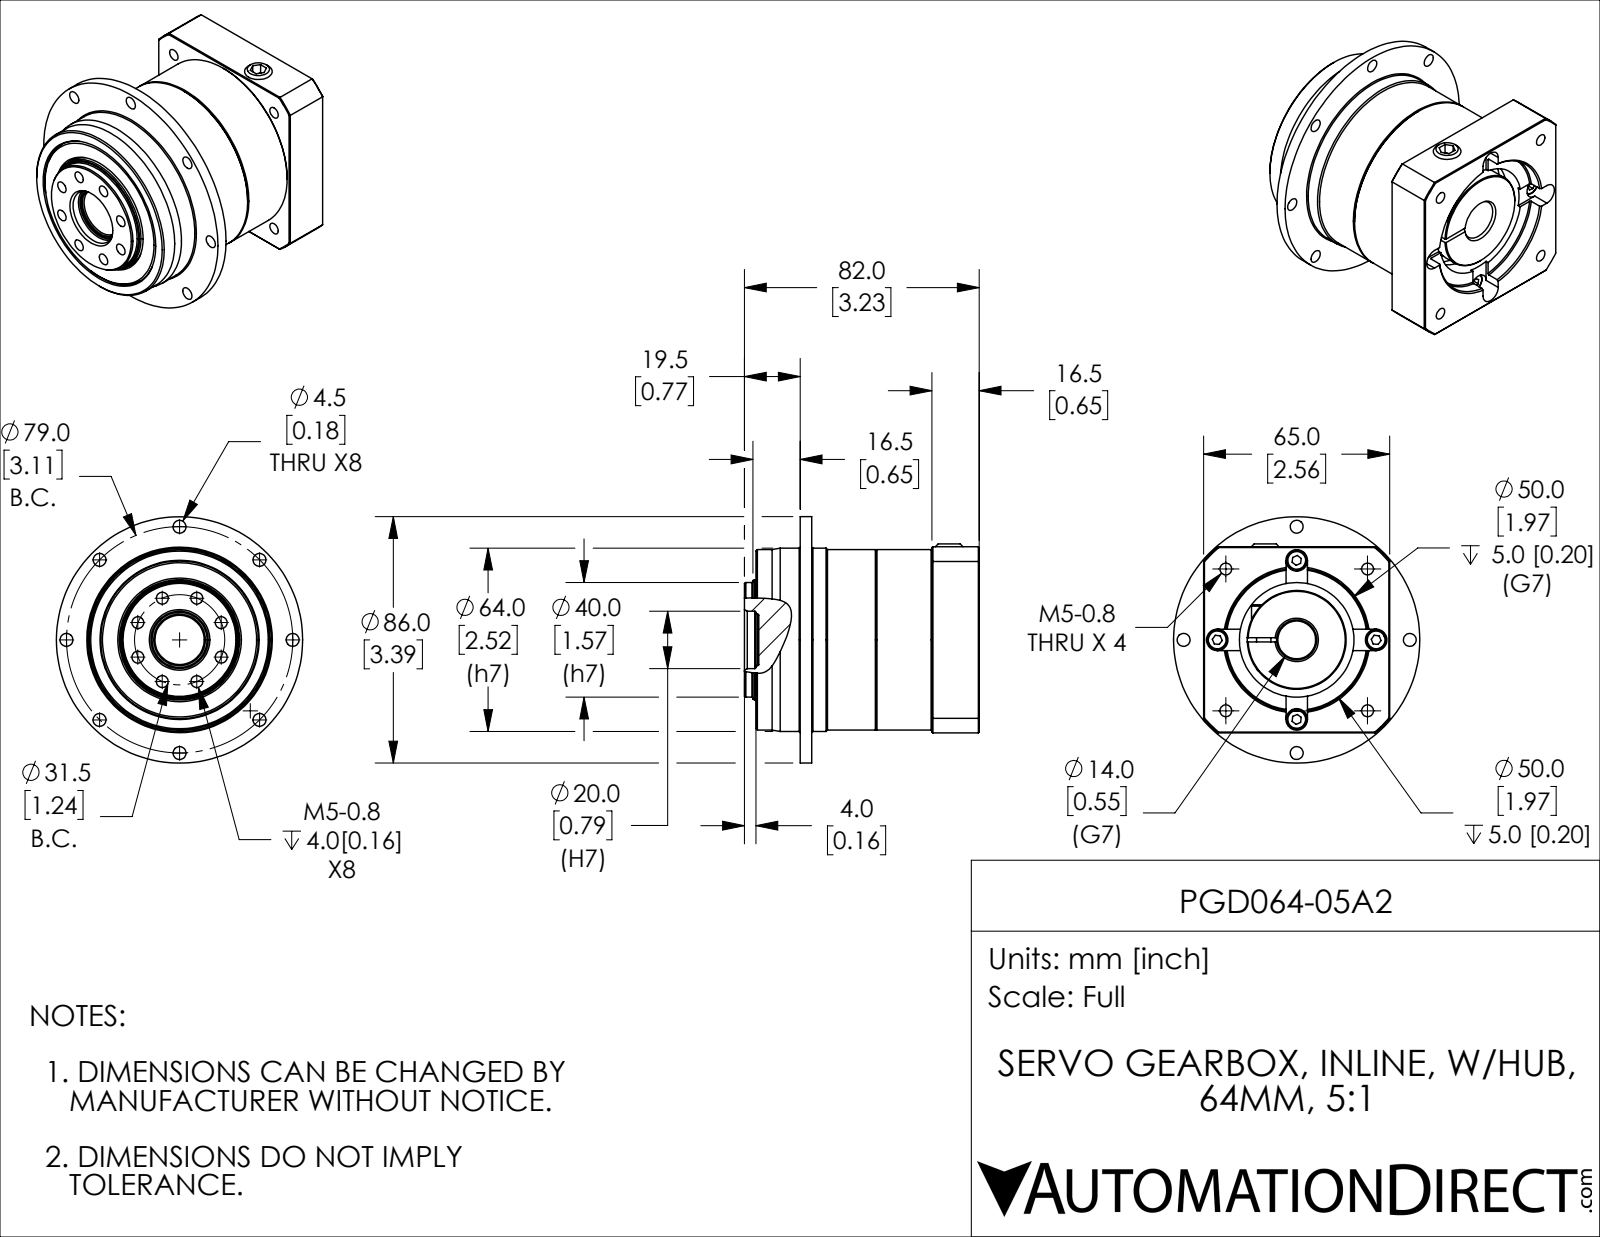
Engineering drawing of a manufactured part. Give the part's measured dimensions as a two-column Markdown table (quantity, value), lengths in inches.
| quantity | value |
| --- | --- |
| part name | PGD064-05A2 |
| STEP written by | SolidWorks 2015 (AUTOMOTIVE_DESIGN) |
| units | inches |
| bodies | 10 solids, 372 faces (127 planar, 150 cylindrical, 95 other) |
| overall size | 3.386 × 3.386 × 3.228 |
| volume | 15.35 in³ |
| surface area | 65.52 in² |
| round holes (diameter × count) | 0.163 × 12, 0.177 × 9, 0.295 × 4, 0.197 × 2, 0.128 × 1, 0.157 × 1, 0.315 × 1, 0.551 × 1, 0.787 × 1, 1.575 × 1, 1.969 × 1 |
| round bosses / shafts (diameter × count) | 3.386 × 1, 2.52 × 1, 2.48 × 1, 1.654 × 1, 1.142 × 1, 0.276 × 1, 0.157 × 1 |
| partial cylindrical surfaces (radius × count) | 1.673 × 1 |
| main face-to-face distances | 0.157, 2.461, 2.559, 2.303, 0.65, 0.748, 3.209, 0.906, 0.039, 0.768 |
| hole center spacings | 1.437, 2.141, 0.62, 0.571, 0.839, 0.877, 0.981, 1.01 |
